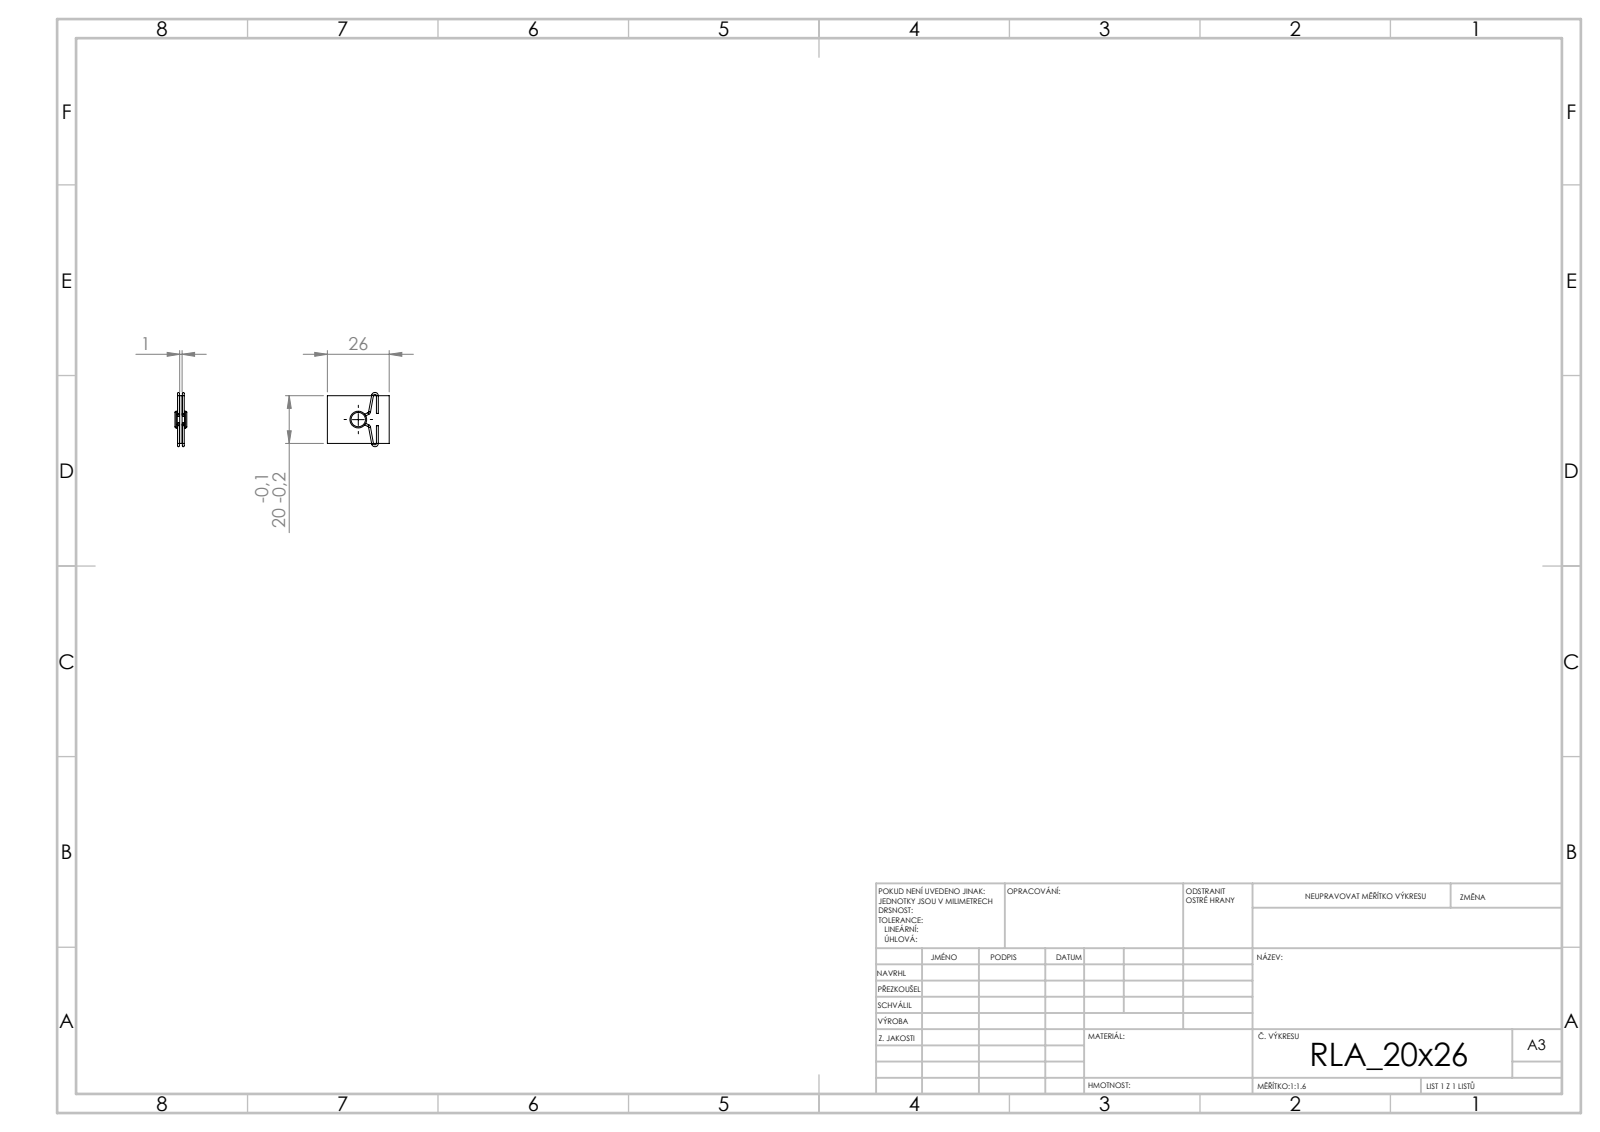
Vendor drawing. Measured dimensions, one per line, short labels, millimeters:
written by: SolidWorks 2019 (CONFIG_CONTROL_DESIGN)
unit: mm
bodies: 3 solids, 82 faces (14 planar, 40 cylindrical, 28 other)
size: 26 × 22.8 × 5
volume: 674 mm³; area: 1 567 mm²
bosses: 14× ⌀0.8, 1× ⌀7, 1× ⌀4
face distances: 1, 2, 3, 4, 5, 20, 26, 7.45, 12.55, 5.1
